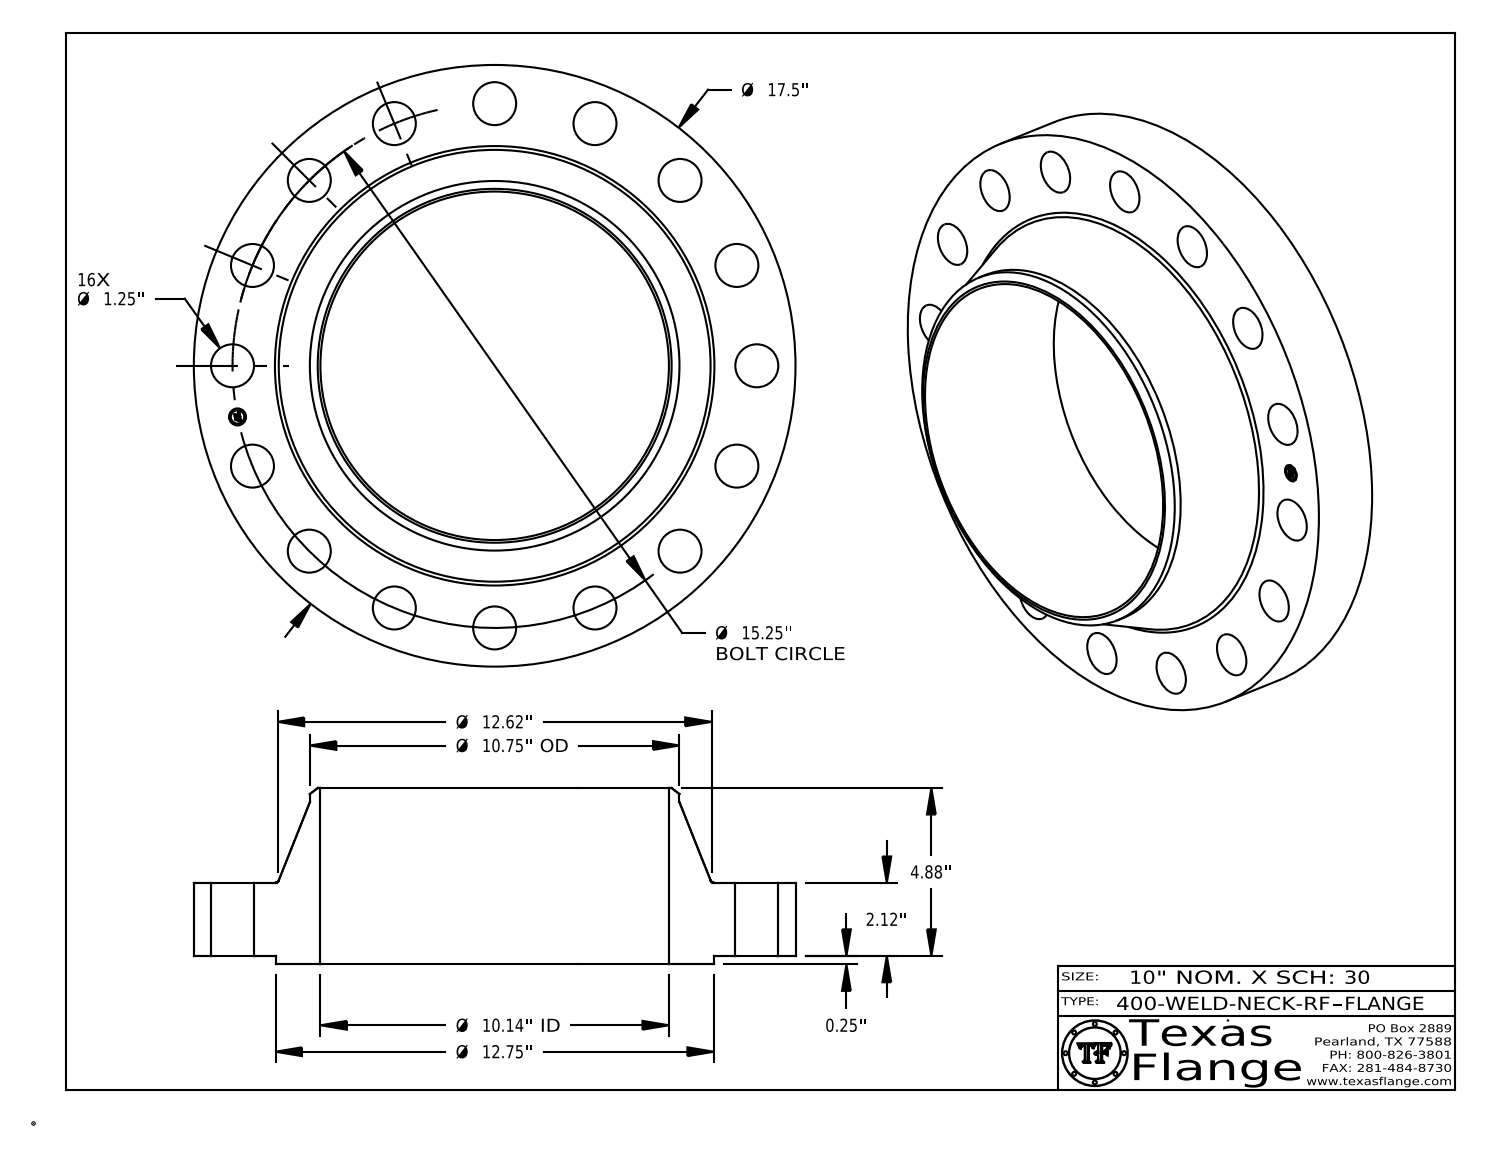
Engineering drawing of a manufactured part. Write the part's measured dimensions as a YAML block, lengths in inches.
part_name: "400-WELD-NECK-RF"
step_written_by: "CATIA V5 STEP AP214 (AUTOMOTIVE_DESIGN)"
units: inches
bodies: {solids: 1, faces: 435, planar: 369, cylindrical: 60, other: 6}
overall_size: [17.5, 17.5, 5.13]
volume: 375.4
surface_area: 771.3
round_holes:
  - {diameter: 1.25, count: 16}
  - {diameter: 0.495, count: 1}
  - {diameter: 10.136, count: 1}
round_bosses_or_shafts:
  - {diameter: 0.03, count: 8}
  - {diameter: 17.5, count: 1}
  - {diameter: 12.75, count: 1}
  - {diameter: 10.75, count: 1}
  - {diameter: 0.39, count: 1}
face_to_face_distances: [2.12, 0.25, 2.37, 5.13, 4.88, 2.76, 0.015, 2.355, 2.105, 2.775]
hole_center_spacings: [8.472, 10.783, 14.957, 14.089, 7.625, 2.975, 2.975, 5.836]
